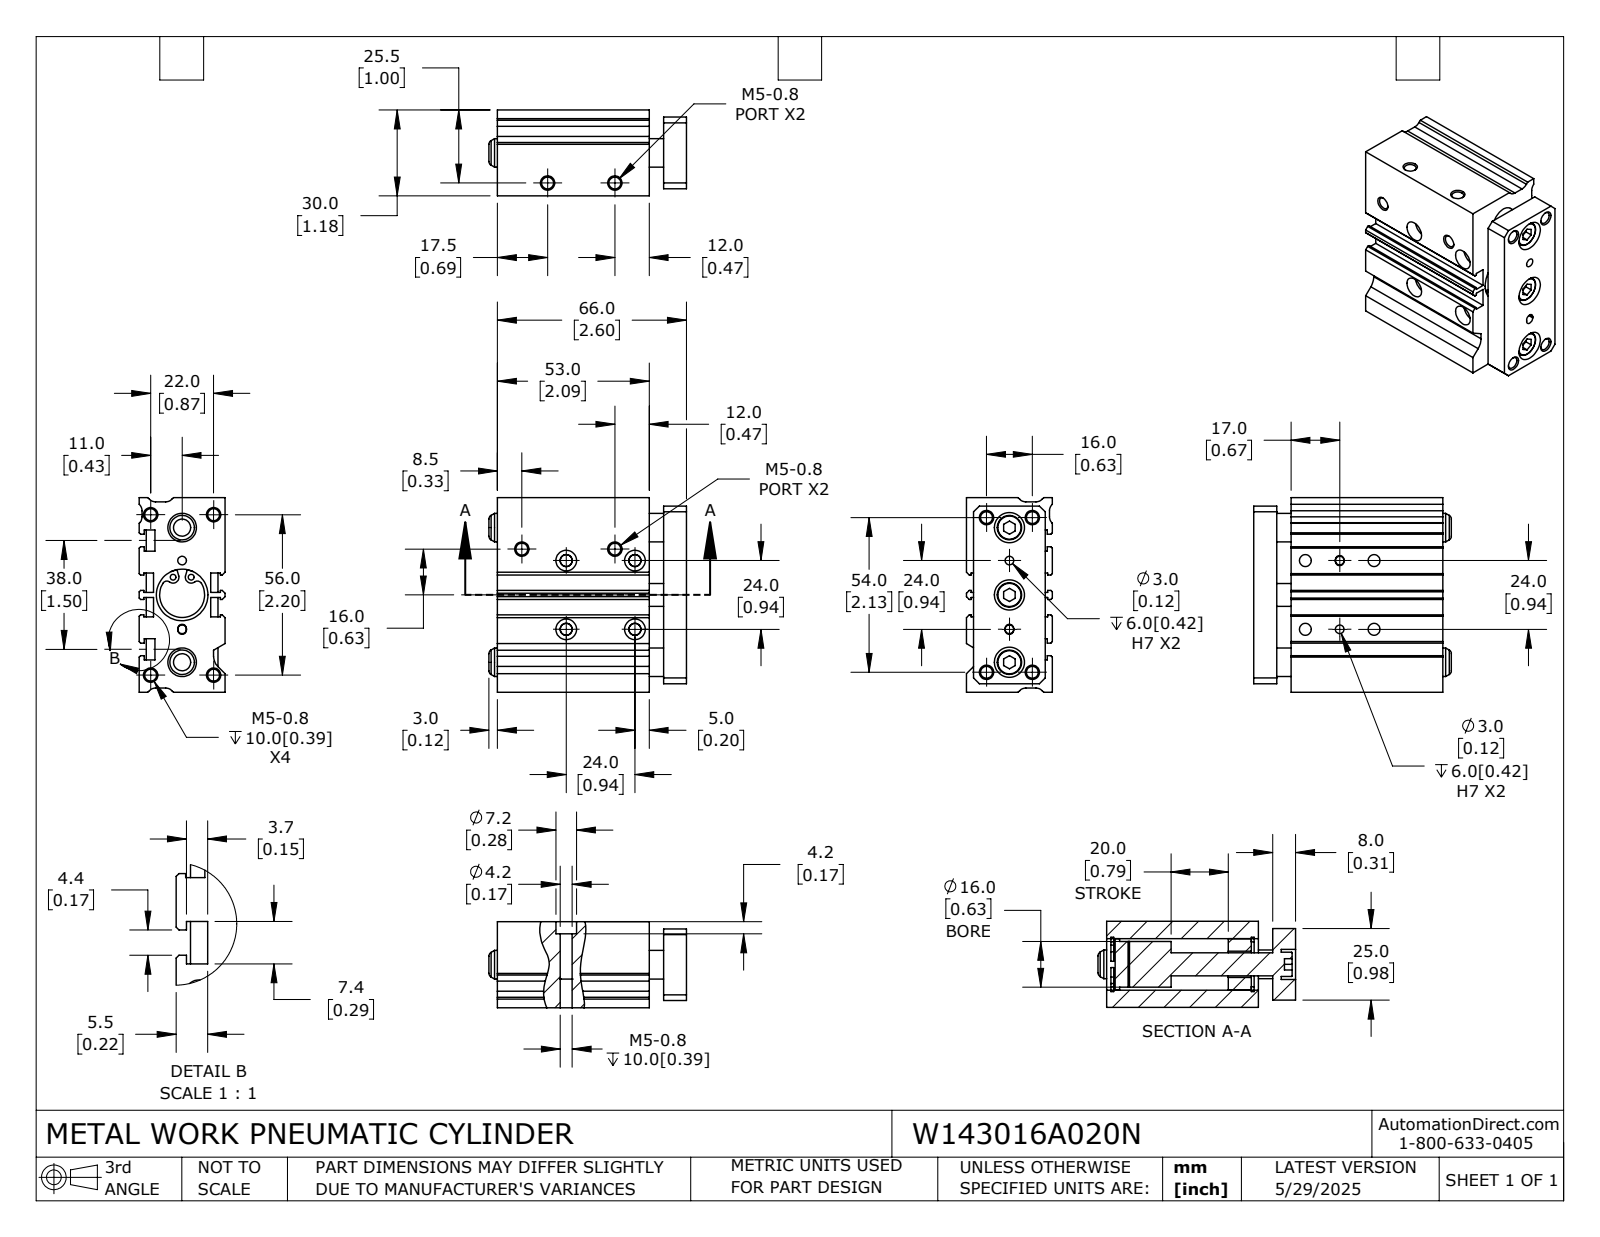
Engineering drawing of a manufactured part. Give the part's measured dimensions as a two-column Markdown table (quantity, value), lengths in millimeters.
| quantity | value |
| --- | --- |
| part name | W143016A020N; W143016A020_BODY; W143016A020_ROD |
| STEP written by | SolidWorks 2024 (CONFIG_CONTROL_DESIGN) |
| units | millimeters |
| bodies | 6 solids, 344 faces (169 planar, 137 cylindrical, 38 other) |
| overall size | 69 × 68 × 30 |
| volume | 97 719 mm³ |
| surface area | 40 714 mm² |
| round holes (diameter × count) | 4.13 × 16, 2 × 4, 3 × 4, 4.2 × 4, 7.2 × 4, 10.5 × 3, 10 × 2, 9.2 × 1, 15.7 × 1 |
| round bosses / shafts (diameter × count) | 8.5 × 3, 19 × 2, 18 × 1, 16 × 1, 8 × 1 |
| partial cylindrical surfaces (radius × count) | 3 × 6, 1.5 × 4, 1.58 × 4, 2.07 × 4, 5 × 1 |
| main face-to-face distances | 5, 2.5, 25, 30, 8, 58, 1.5, 53, 3, 13 |
| hole center spacings | 12, 24, 3.16, 6.62, 6.95, 8.73, 11.88, 17 |
